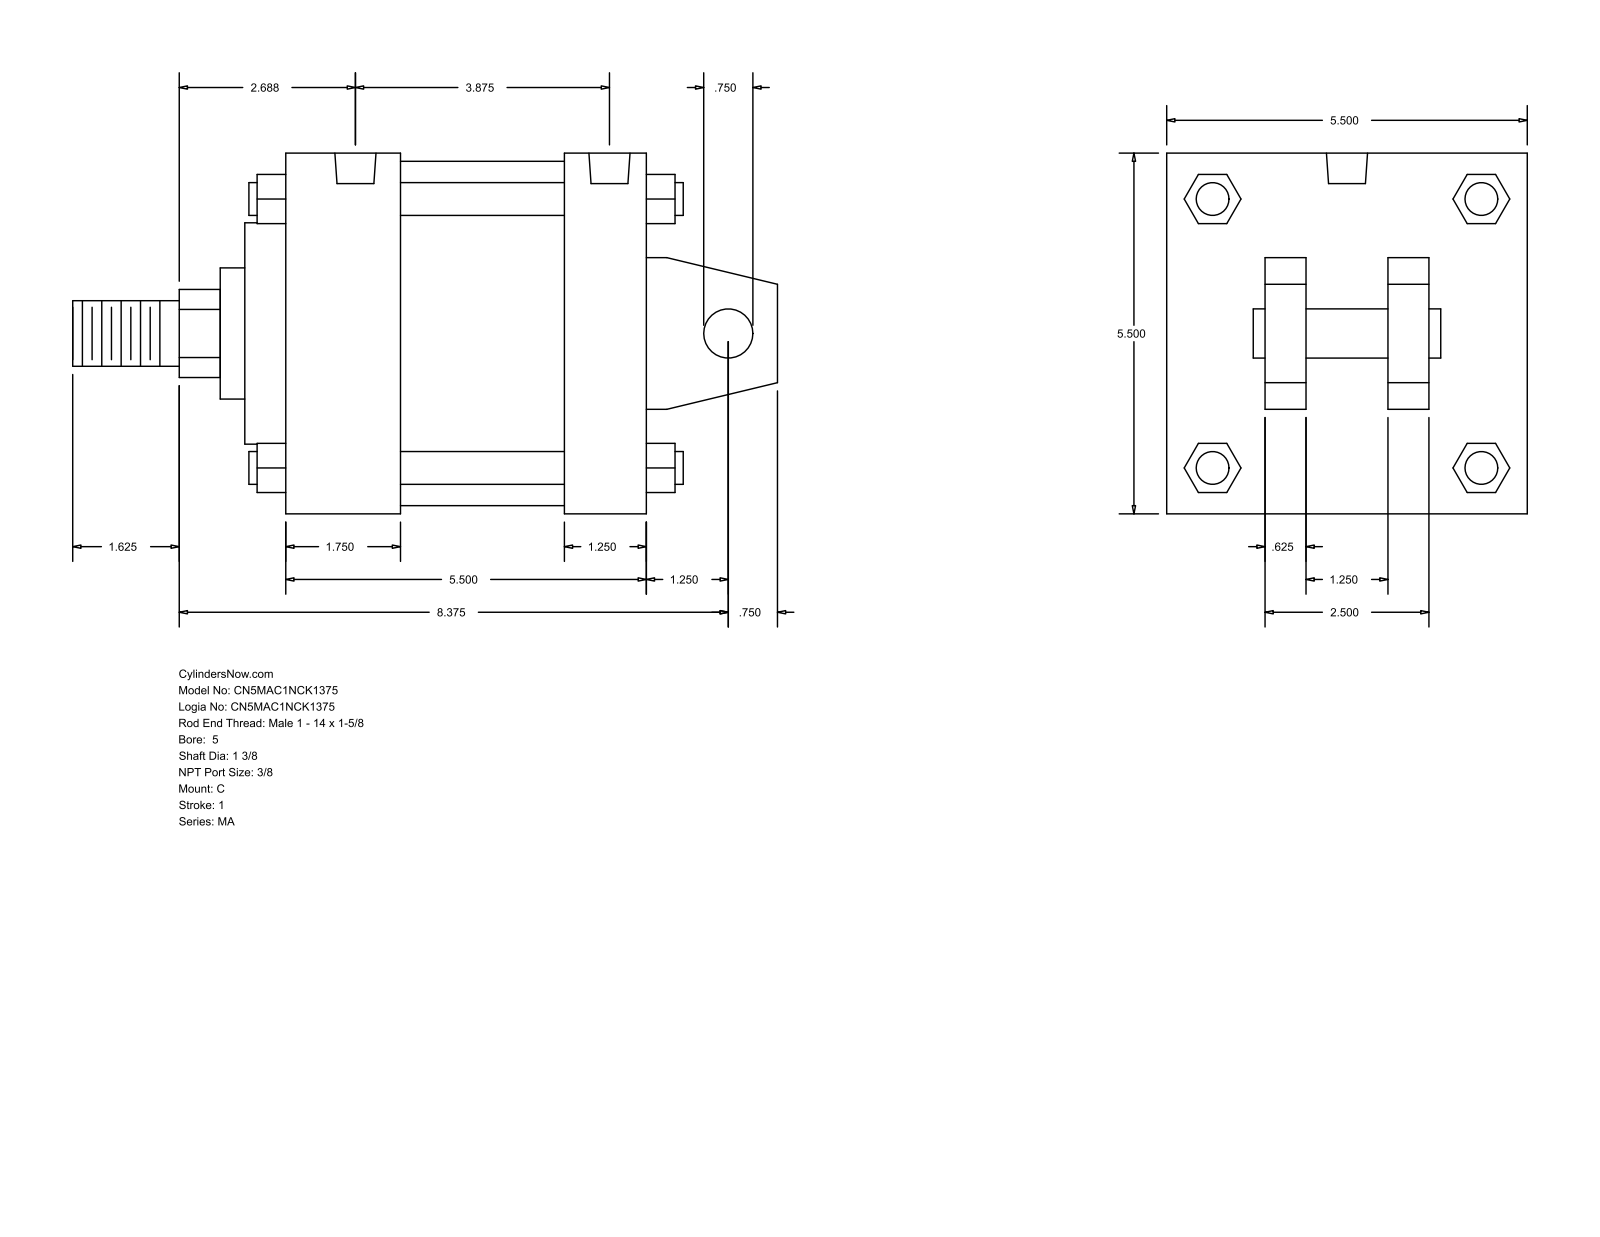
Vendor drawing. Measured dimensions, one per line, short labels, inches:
name: MA_C__0500_1.375
written by: GSSL Pune (CONFIG_CONTROL_DESIGN)
unit: in
bodies: 0 solids, 141 faces (109 planar, 32 cylindrical, 0 other)
size: 10.75 × 5.5 × 5.5
holes: 4× ⌀0.437, 2× ⌀0.627
bosses: 4× ⌀0.5, 1× ⌀5.25, 1× ⌀3.375, 1× ⌀2, 1× ⌀1.375, 1× ⌀1, 1× ⌀0.75
rounds: 1× R0.672
face distances: 5.5, 0.625, 2.5, 4.25, 1.25, 1.75, 3.75, 2.125, 1.5, 4
hole spacings: 3.5, 0.187, 0.188, 3.687, 3.688, 3.875
